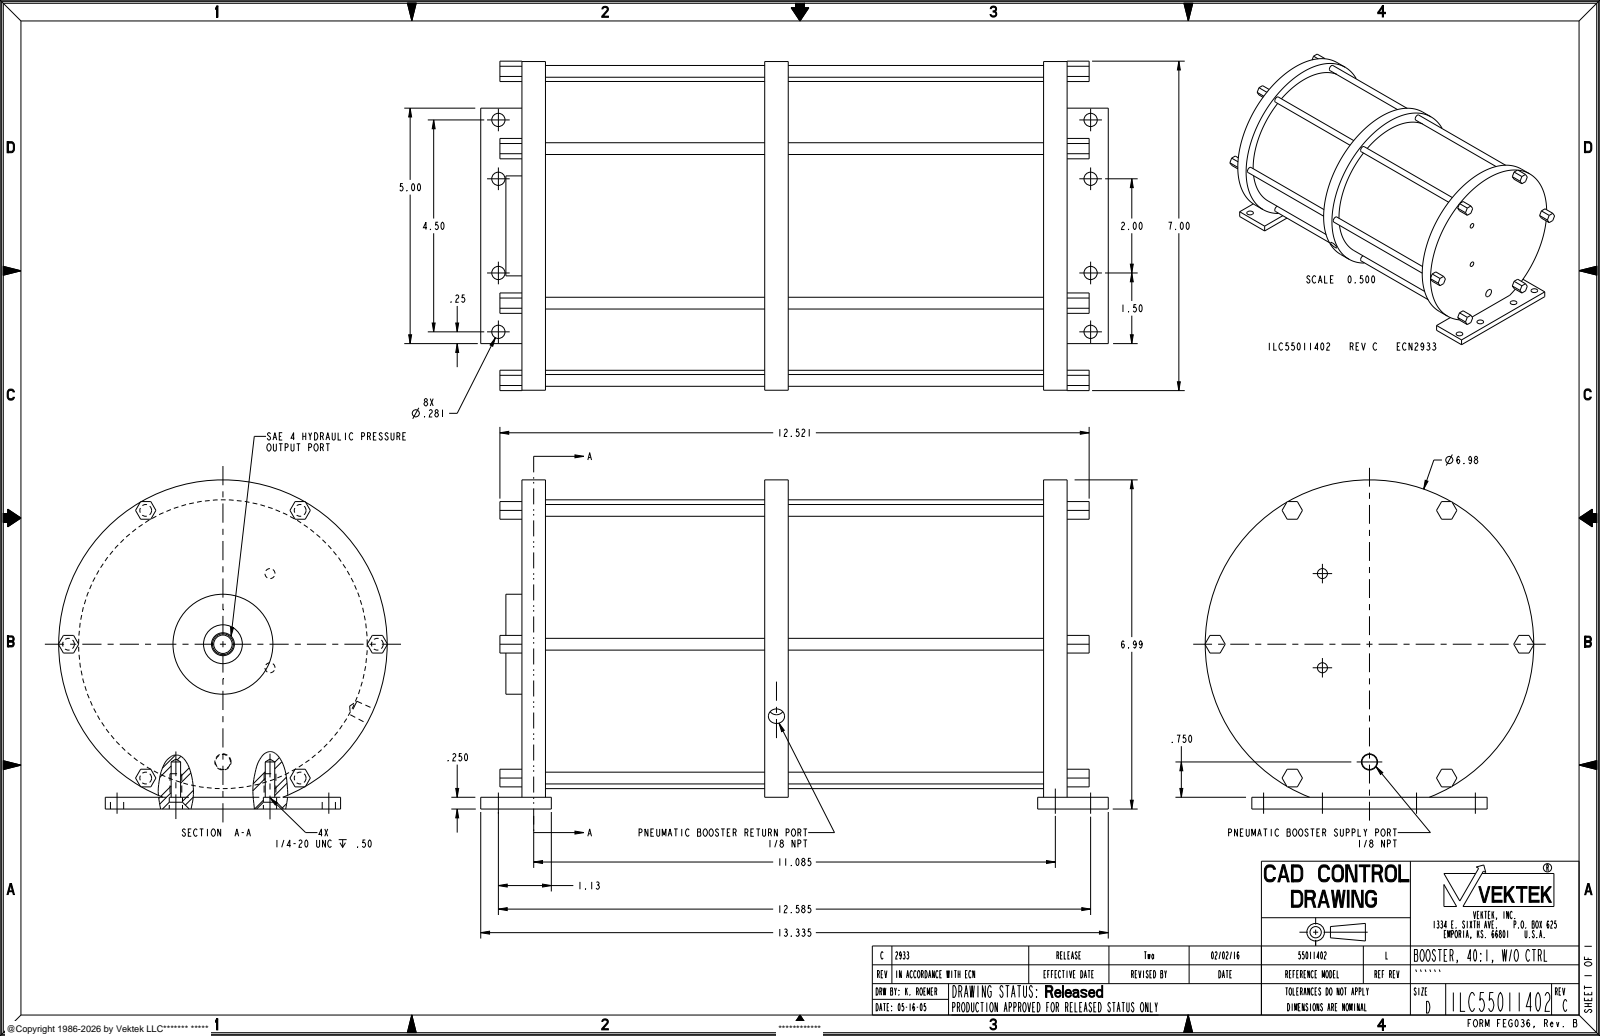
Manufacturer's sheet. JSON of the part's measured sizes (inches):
{"part_name": "ILC55011402", "step_written_by": "PRO/ENGINEER BY PARAMETRIC TECHNOLOGY CORPORATION, 2013320 (CONFIG_CONTROL_DESIGN)", "units": "inches", "bodies": {"solids": 1, "faces": 245, "planar": 128, "cylindrical": 87, "other": 30}, "overall_size": [13.335, 6.996, 6.99], "volume_in3": 362.8, "surface_area_in2": 431.9, "round_holes": [[0.281, 12], [0.25, 6], [0.201, 4], [0.213, 2], [0.392, 1], [0.825, 1]], "round_bosses_or_shafts": [[0.25, 6], [6.98, 1], [6.133, 1], [2.123, 1], [0.437, 1]], "face_to_face_distances": [11.585, 0.5, 11.085, 5.159, 5.926, 0.25, 5.659, 4.659, 10.585, 6.426], "hole_center_spacings": [2, 0.75, 1.25, 1.458, 2.136, 3.25, 3.335, 11.835]}
